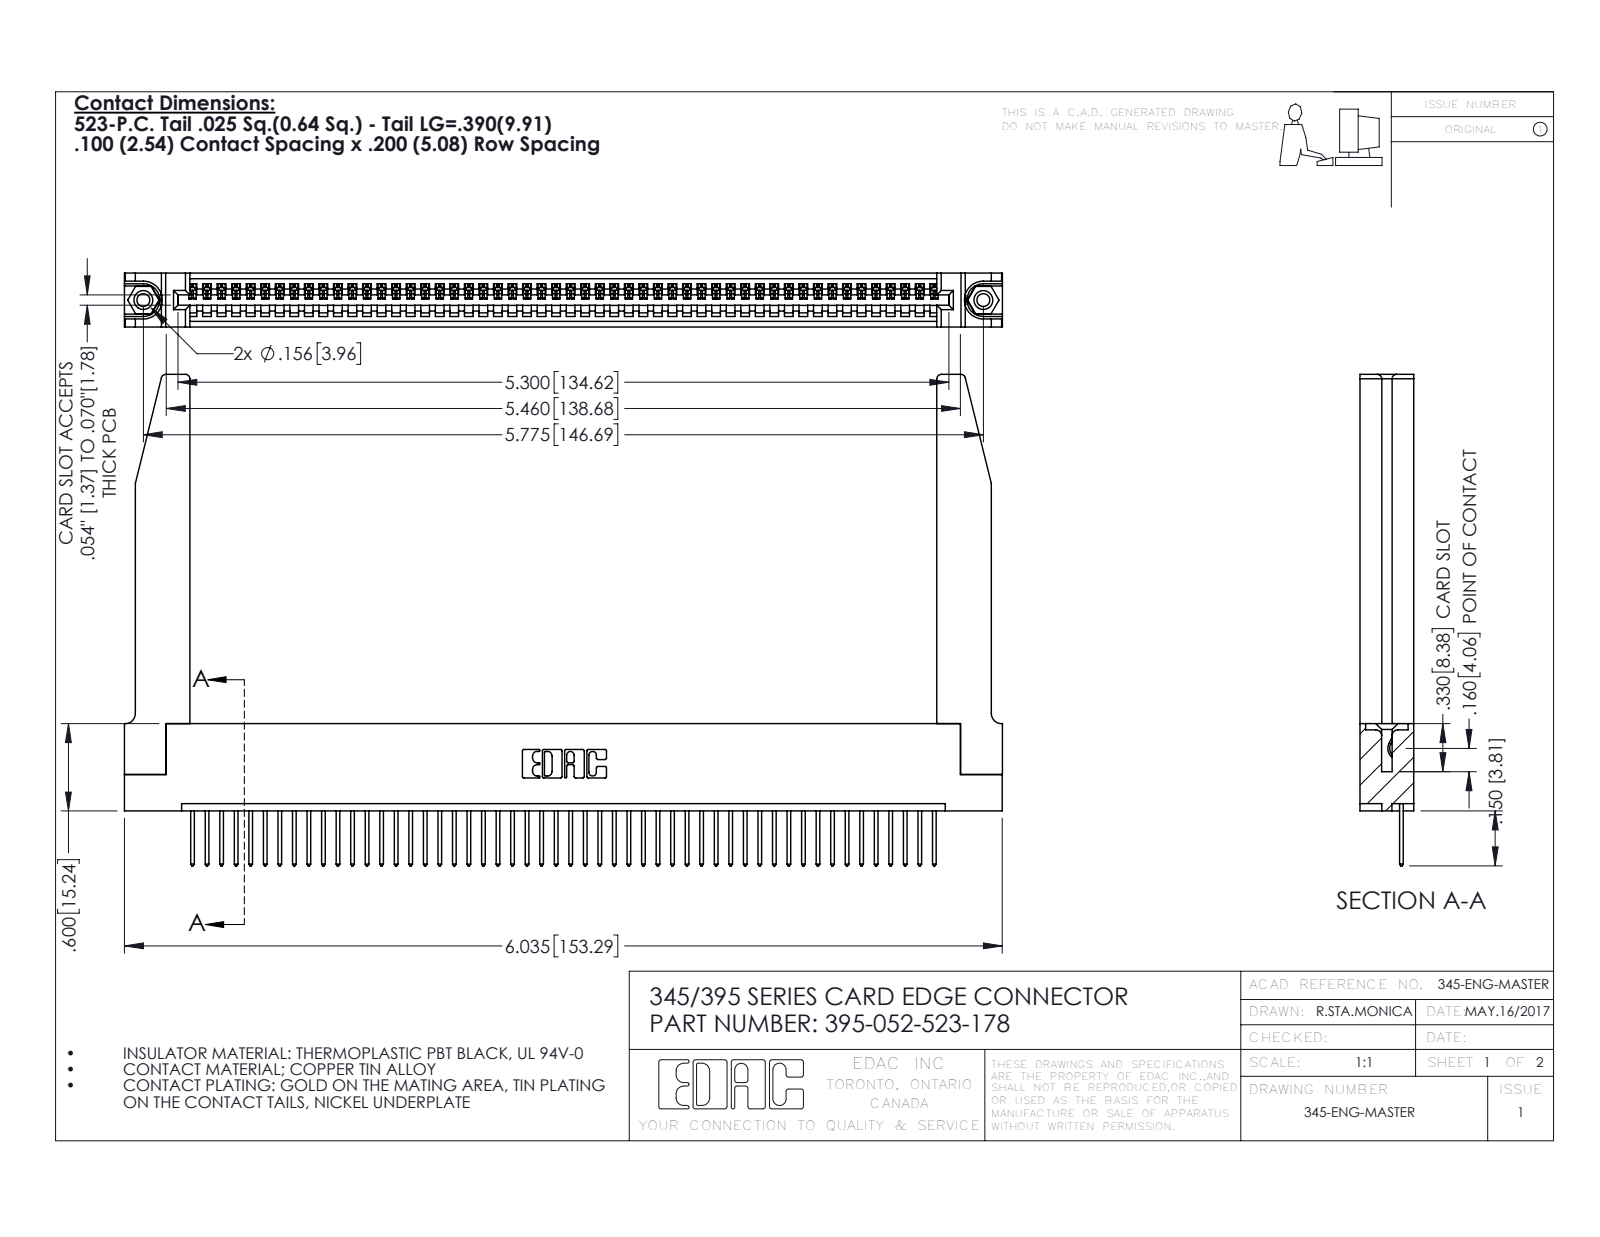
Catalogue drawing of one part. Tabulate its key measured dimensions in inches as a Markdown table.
| quantity | value |
| --- | --- |
| part name | 345 Part_Flush Mounting Lugs - 0.156 Dia-TH; 345-220-078_345-220-078; 345-292-001_345-293-123; 345-250-001_345-250-001-102 (+1 more) |
| STEP written by | SolidWorks 2016 (CONFIG_CONTROL_DESIGN) |
| units | inches |
| bodies | 57 solids, 3376 faces (2302 planar, 1022 cylindrical, 52 other) |
| overall size | 6.036 × 3.377 × 0.37 |
| volume | 1.367 in³ |
| surface area | 41.03 in² |
| round holes (diameter × count) | 0.089 × 2, 0.125 × 2, 0.156 × 2, 0.064 × 1 |
| round bosses / shafts (diameter × count) | 0.155 × 2 |
| partial cylindrical surfaces (radius × count) | 0.006 × 104, 0.01 × 104, 0.01 × 22, 0.03 × 8, 0.007 × 6, 0.031 × 6, 0.026 × 3, 0.031 × 2 |
| main face-to-face distances | 0.072, 0.37, 0.298, 0.2, 0.098, 0.272, 0.025, 0.225, 0.15, 0.148 |
| hole center spacings | 0.27, 5.539, 5.775 |
